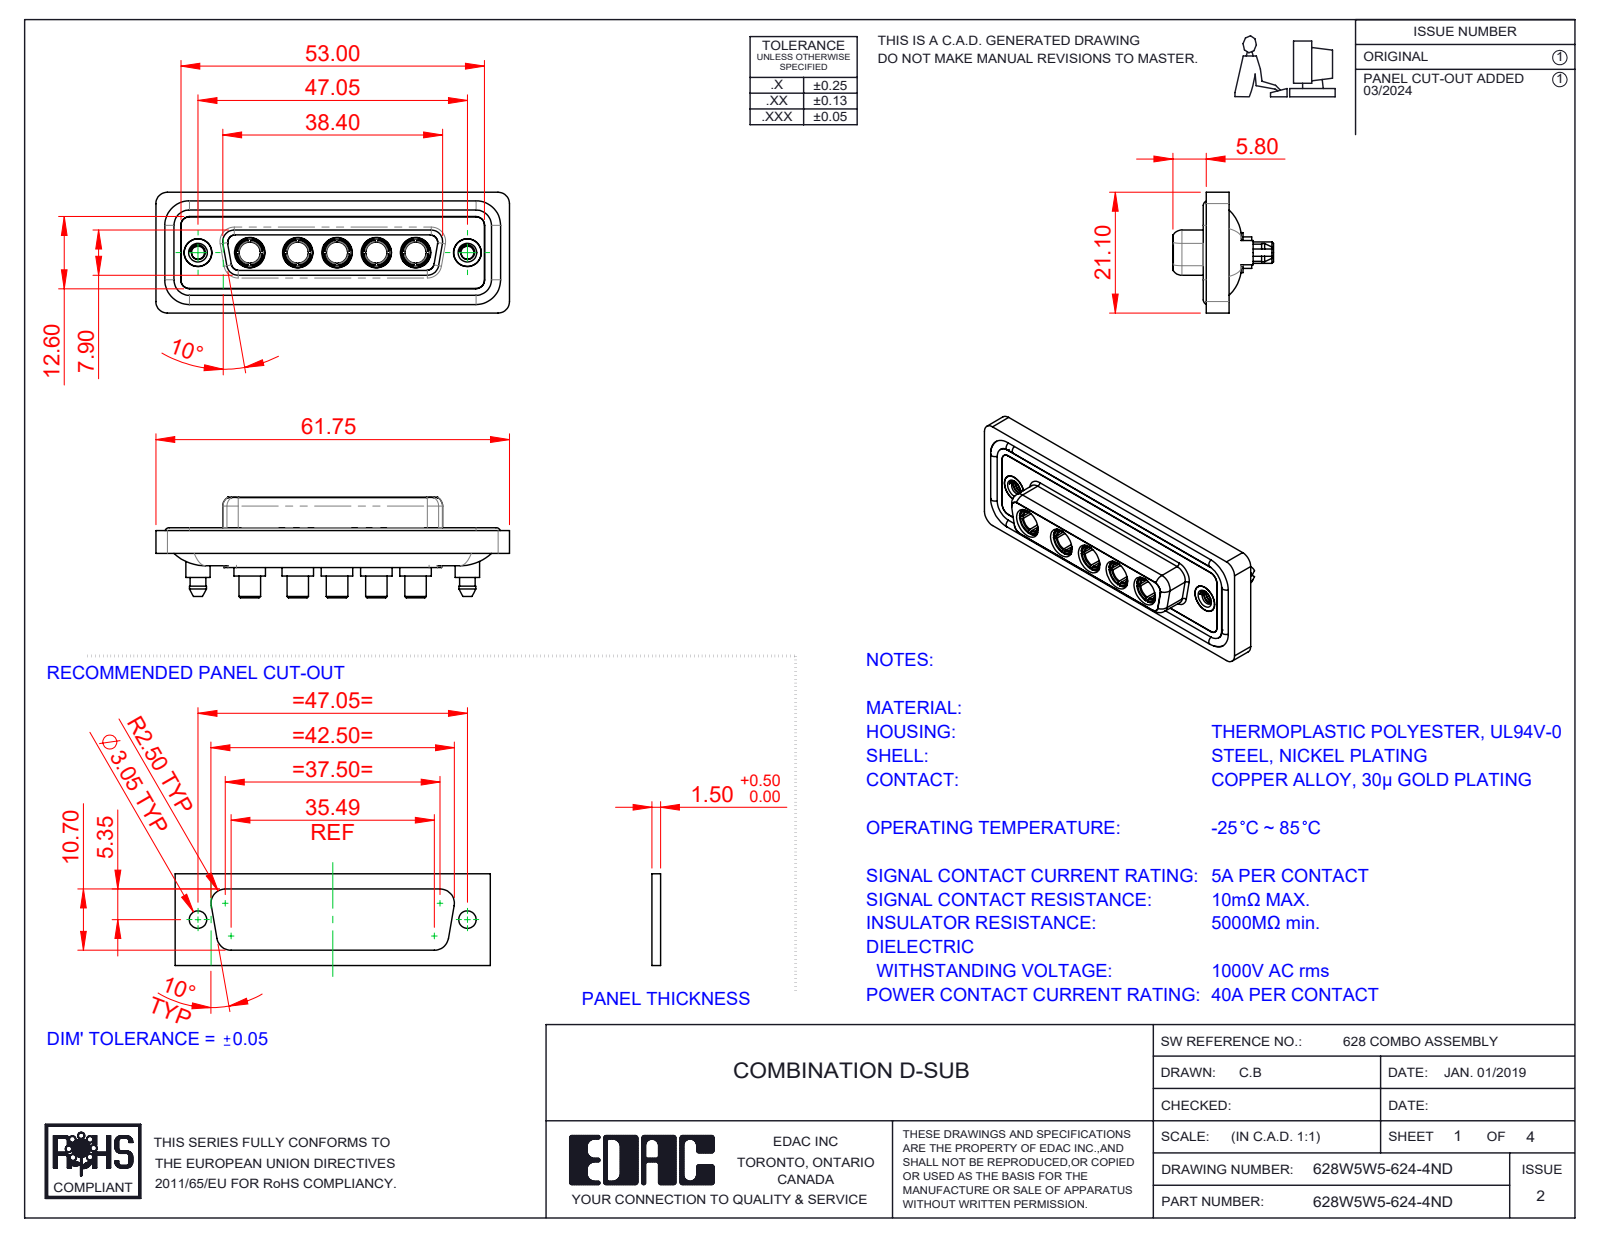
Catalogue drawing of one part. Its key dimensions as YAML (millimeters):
part_name: "628Combo Housing_5W5; 628Combo Shell Rear_25 Contacts; 628Combo Threaded Boardlock_D; 628Combo Shell Front_25 Contacts (+3 more)"
step_written_by: "SolidWorks 2023 (CONFIG_CONTROL_DESIGN)"
units: millimeters
bodies: {solids: 17, faces: 822, planar: 266, cylindrical: 351, other: 205}
overall_size: [61.75, 21.1, 17.55]
volume: 8400
surface_area: 13809
round_holes:
  - {diameter: 4.85, count: 7}
  - {diameter: 3.7, count: 5}
  - {diameter: 5.3, count: 5}
  - {diameter: 2.26, count: 2}
  - {diameter: 4, count: 2}
  - {diameter: 4.05, count: 2}
  - {diameter: 5, count: 2}
round_bosses_or_shafts:
  - {diameter: 5.5, count: 5}
  - {diameter: 5.2, count: 5}
  - {diameter: 4.96, count: 5}
  - {diameter: 4.75, count: 5}
  - {diameter: 3.75, count: 5}
  - {diameter: 1.6, count: 4}
  - {diameter: 5.4, count: 2}
  - {diameter: 4.95, count: 2}
partial_cylinders:
  - {radius: 1.5, count: 24}
  - {radius: 2, count: 18}
  - {radius: 1.6, count: 10}
  - {radius: 1.35, count: 8}
  - {radius: 2.1, count: 5}
  - {radius: 0.25, count: 4}
  - {radius: 0.5, count: 4}
  - {radius: 0.6, count: 4}
face_to_face_distances: [0.4, 1.8, 7.45, 5.65, 0.5, 7.05, 6.6, 1.6, 1.1, 2.9]
hole_center_spacings: [6.86, 9.04, 13.72, 38.01, 8.39, 15.25, 15.9, 17.43]
